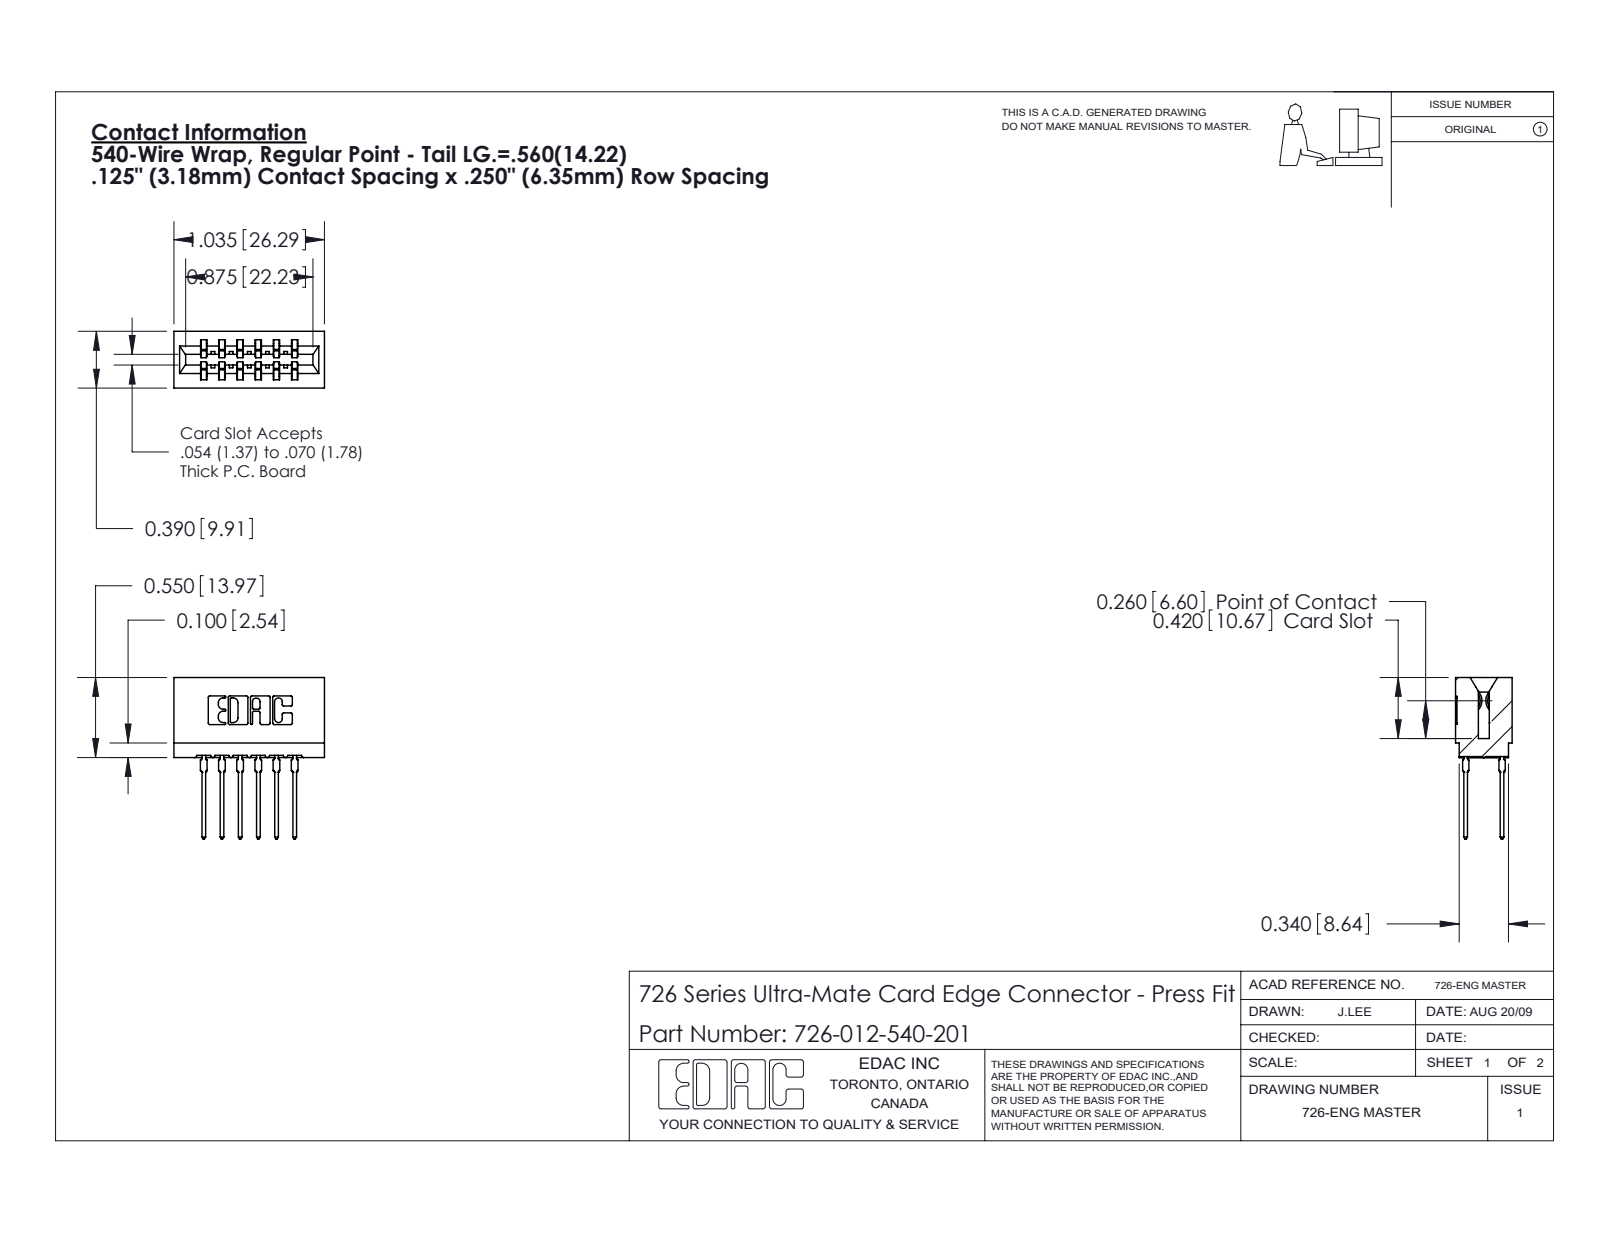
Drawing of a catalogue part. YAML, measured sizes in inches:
part_name: "746-292-001_540; 726 Part_.515 Slot Depth - 01; 726-012-540-201"
step_written_by: "SolidWorks 2020 (CONFIG_CONTROL_DESIGN)"
units: inches
bodies: {solids: 13, faces: 1171, planar: 607, cylindrical: 252, other: 312}
overall_size: [1.109, 1.035, 0.39]
volume: 0.161
surface_area: 6.106
partial_cylinders:
  - {radius: 0.021, count: 24}
  - {radius: 0.01, count: 22}
  - {radius: 0.005, count: 8}
  - {radius: 0.011, count: 8}
  - {radius: 0.015, count: 7}
  - {radius: 0.007, count: 6}
  - {radius: 0.031, count: 6}
  - {radius: 0.026, count: 3}
face_to_face_distances: [0.25, 0.057, 0.333, 0.125, 0.042, 0.025, 0.083, 0.307, 0.125, 0.375]
